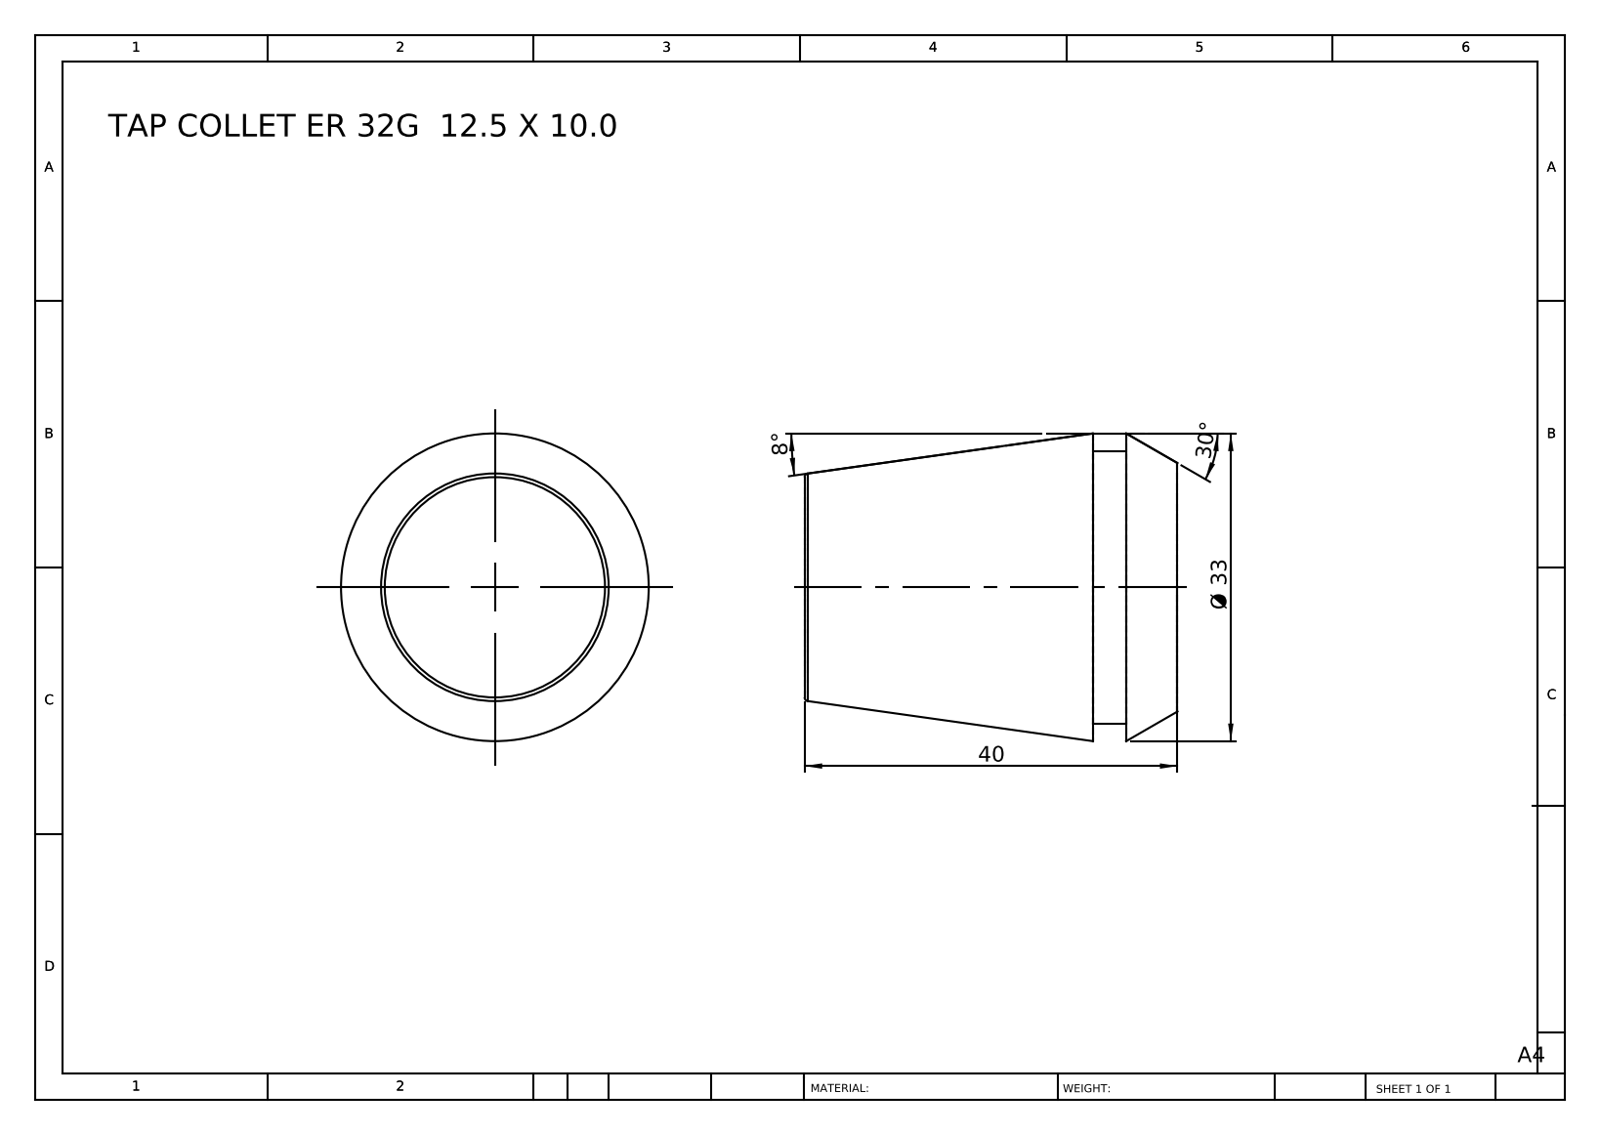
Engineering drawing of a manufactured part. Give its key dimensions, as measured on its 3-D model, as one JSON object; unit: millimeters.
{"part_name": "TAP COLLET ER 32G 12.5 X 10.0", "step_written_by": "SolidWorks 2014 (CONFIG_CONTROL_DESIGN)", "units": "millimeters", "bodies": {"solids": 1, "faces": 12, "planar": 4, "cylindrical": 2, "other": 6}, "overall_size": [40, 33, 33], "volume_mm3": 26350, "surface_area_mm2": 5119, "round_bosses_or_shafts": [[29.2, 1]], "face_to_face_distances": [40, 9.1, 30.9, 5.5, 3.6, 34.5]}
